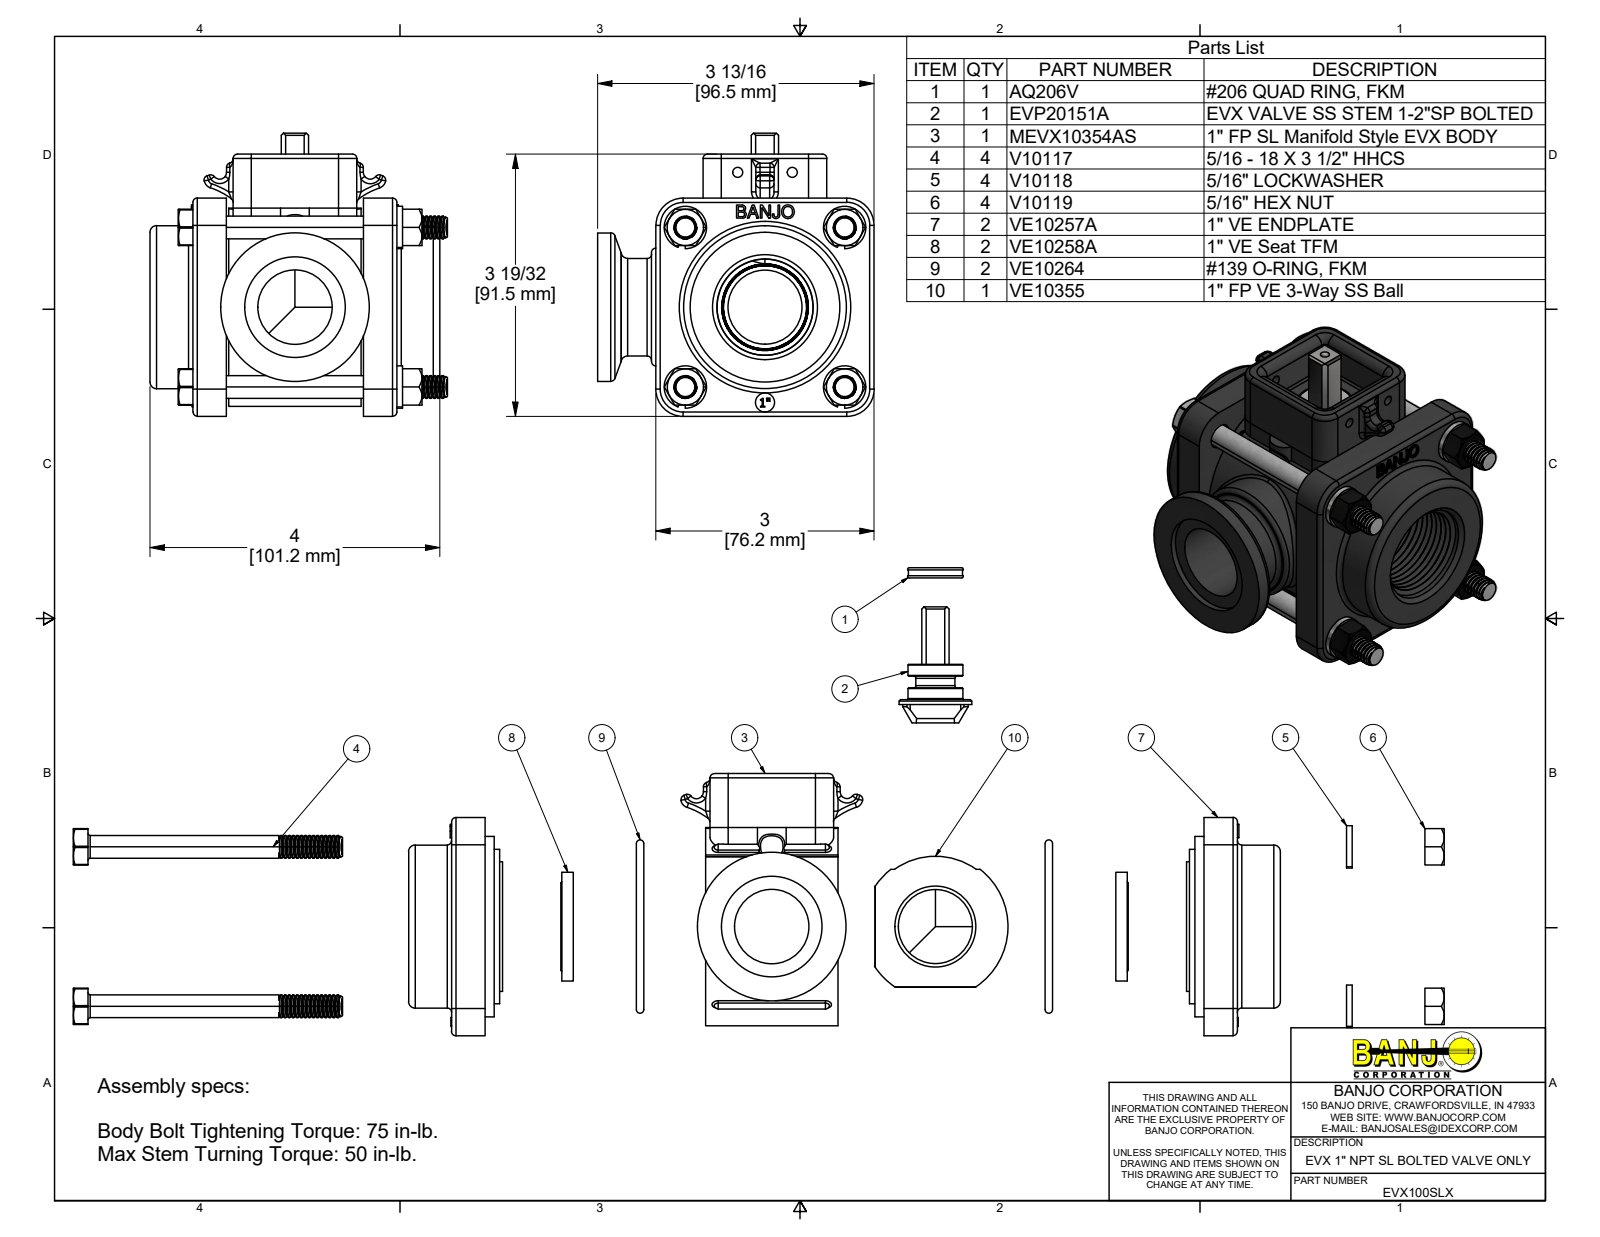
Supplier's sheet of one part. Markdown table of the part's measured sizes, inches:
| quantity | value |
| --- | --- |
| part name | EVX100SLX; MEVX10354AS; MEVX10354ASX; VE10355 (+8 more) |
| STEP written by | Autodesk Inventor 2019 (AUTOMOTIVE_DESIGN) |
| units | inches |
| bodies | 22 solids, 1547 faces (362 planar, 530 cylindrical, 655 other) |
| overall size | 38.771 × 3.893 × 3.8 |
| volume | 21.36 in³ |
| surface area | 351.1 in² |
| round holes (diameter × count) | 0.252 × 4, 0.322 × 4, 0.35 × 4, 1.02 × 3, 0.135 × 2, 0.26 × 1, 0.76 × 1, 1.38 × 1, 1.5 × 1, 2.12 × 1, 2.375 × 1, 2.5 × 1 |
| round bosses / shafts (diameter × count) | 0.268 × 60, 0.583 × 4, 0.313 × 4, 2.725 × 1, 2.48 × 1, 2.24 × 1, 2.124 × 1, 2.04 × 1 |
| partial cylindrical surfaces (radius × count) | 0.06 × 58, 0.03 × 12, 0.134 × 8, 0.375 × 8, 0.125 × 6, 0.21 × 4, 0.25 × 4, 0.284 × 4 |
| main face-to-face distances | 0.46, 2.345, 2.805, 1.885, 3, 0.125, 0.59, 1.05, 2.935, 3.395 |
| hole center spacings | 1.55, 2.192, 1.046, 1.117, 1.891, 2.644, 3.1, 3.186 |
